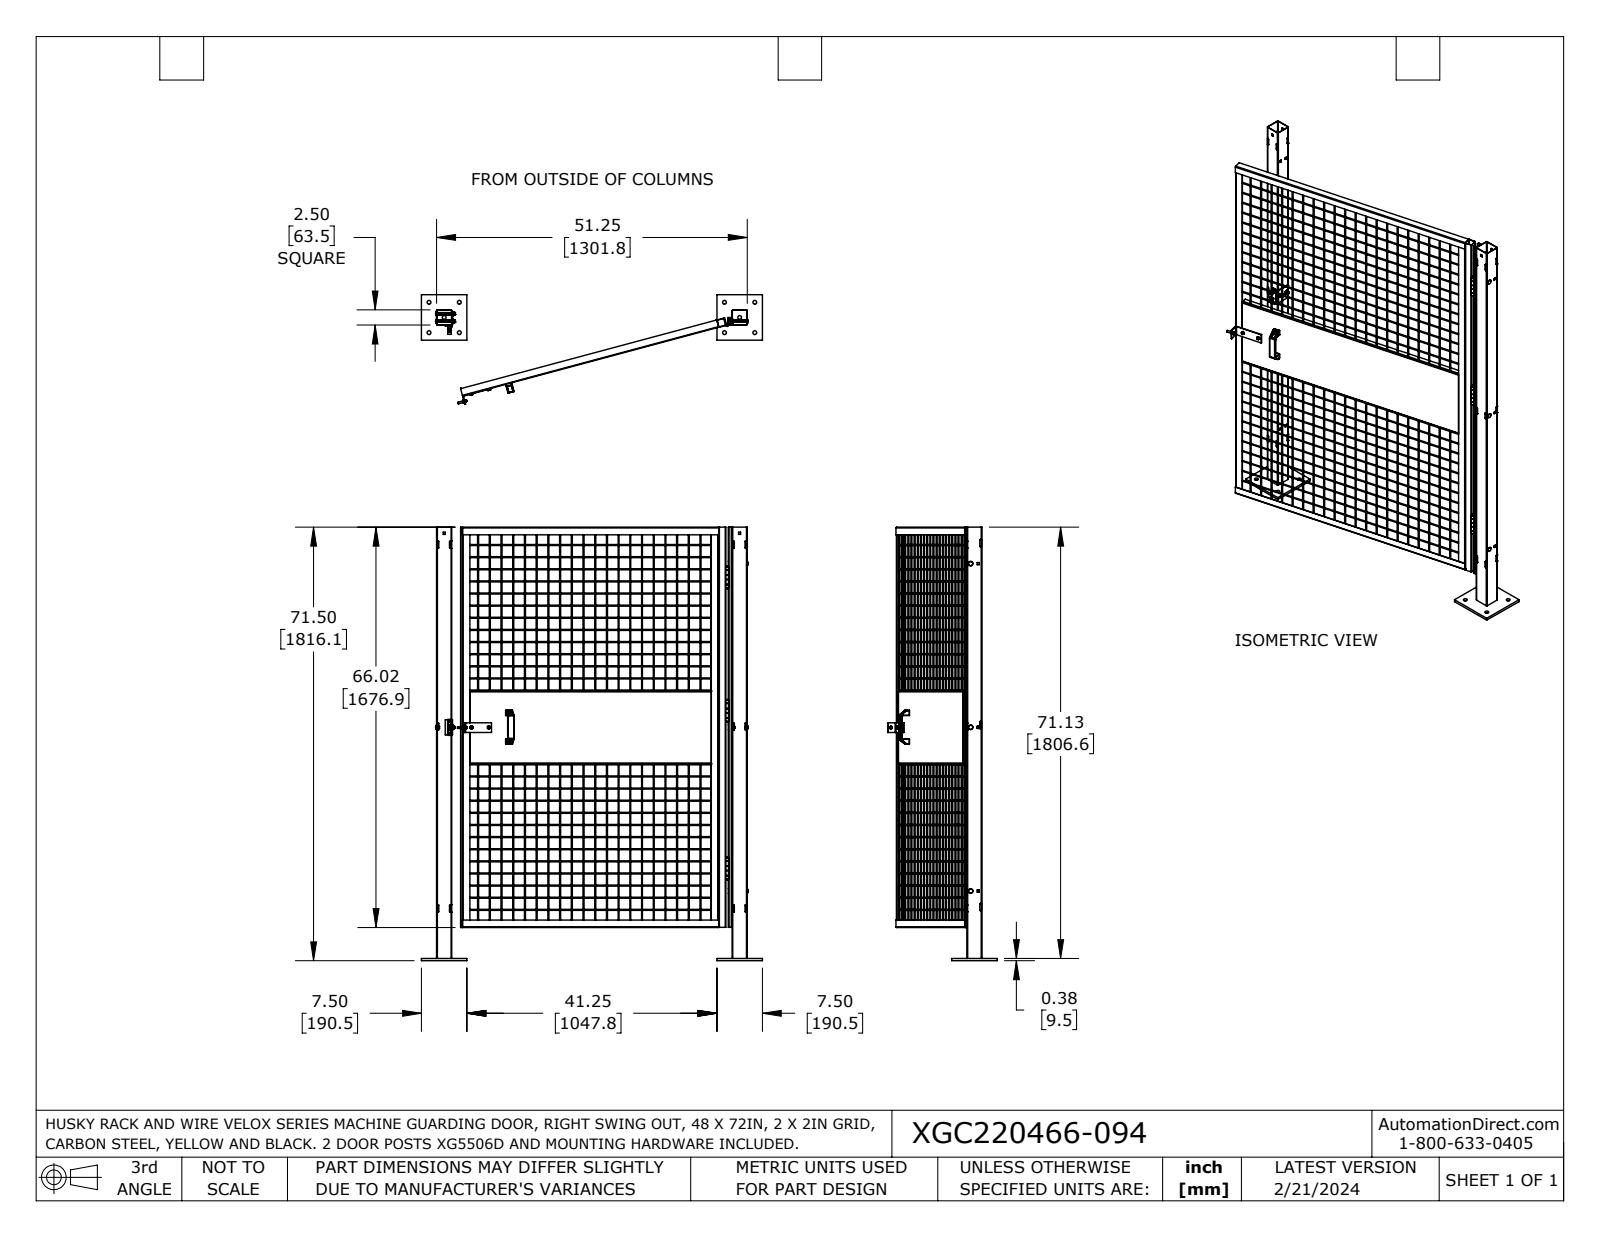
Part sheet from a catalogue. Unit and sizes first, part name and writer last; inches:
Units: inches
Overall size (bounding box): 71.5 × 56.25 × 18.075
Round holes (diameter × count): ⌀0.625 ×10, ⌀0.25 ×6, ⌀0.36 ×6, ⌀0.24 ×5, ⌀0.183 ×4, ⌀0.13 ×2, ⌀0.17 ×2, ⌀0.235 ×2, ⌀0.5 ×2, ⌀0.184 ×1
Round bosses / shafts (diameter × count): ⌀0.164 ×28, ⌀0.16 ×22, ⌀0.687 ×5, ⌀0.318 ×5, ⌀0.594 ×4, ⌀0.252 ×4, ⌀0.276 ×2, ⌀0.158 ×2
Partial cylindrical surfaces — rounded edges, fillets, slot ends (radius × count): R0.13 ×31, R0.05 ×30, R0.007 ×24, R0.12 ×14, R0.062 ×12, R0.063 ×11, R0.025 ×10, R0.125 ×9
Main face-to-face distances: 0.058, 2.442, 0.07, 2.5, 48.75, 2.384, 0.072, 51.192, 48.692, 48.808
Hole centre spacings: 3.535, 5, 48.75, 4.803, 7.071, 46.317, 49.006, 51.311
Volume: 288 in³ · Surface area: 7 542 in²
Bodies: 49 solids, 1585 faces (926 planar, 420 cylindrical, 239 other)
Part name (STEP PRODUCT): XGC220466-094
STEP written by: SolidWorks 2023 (AUTOMOTIVE_DESIGN)
